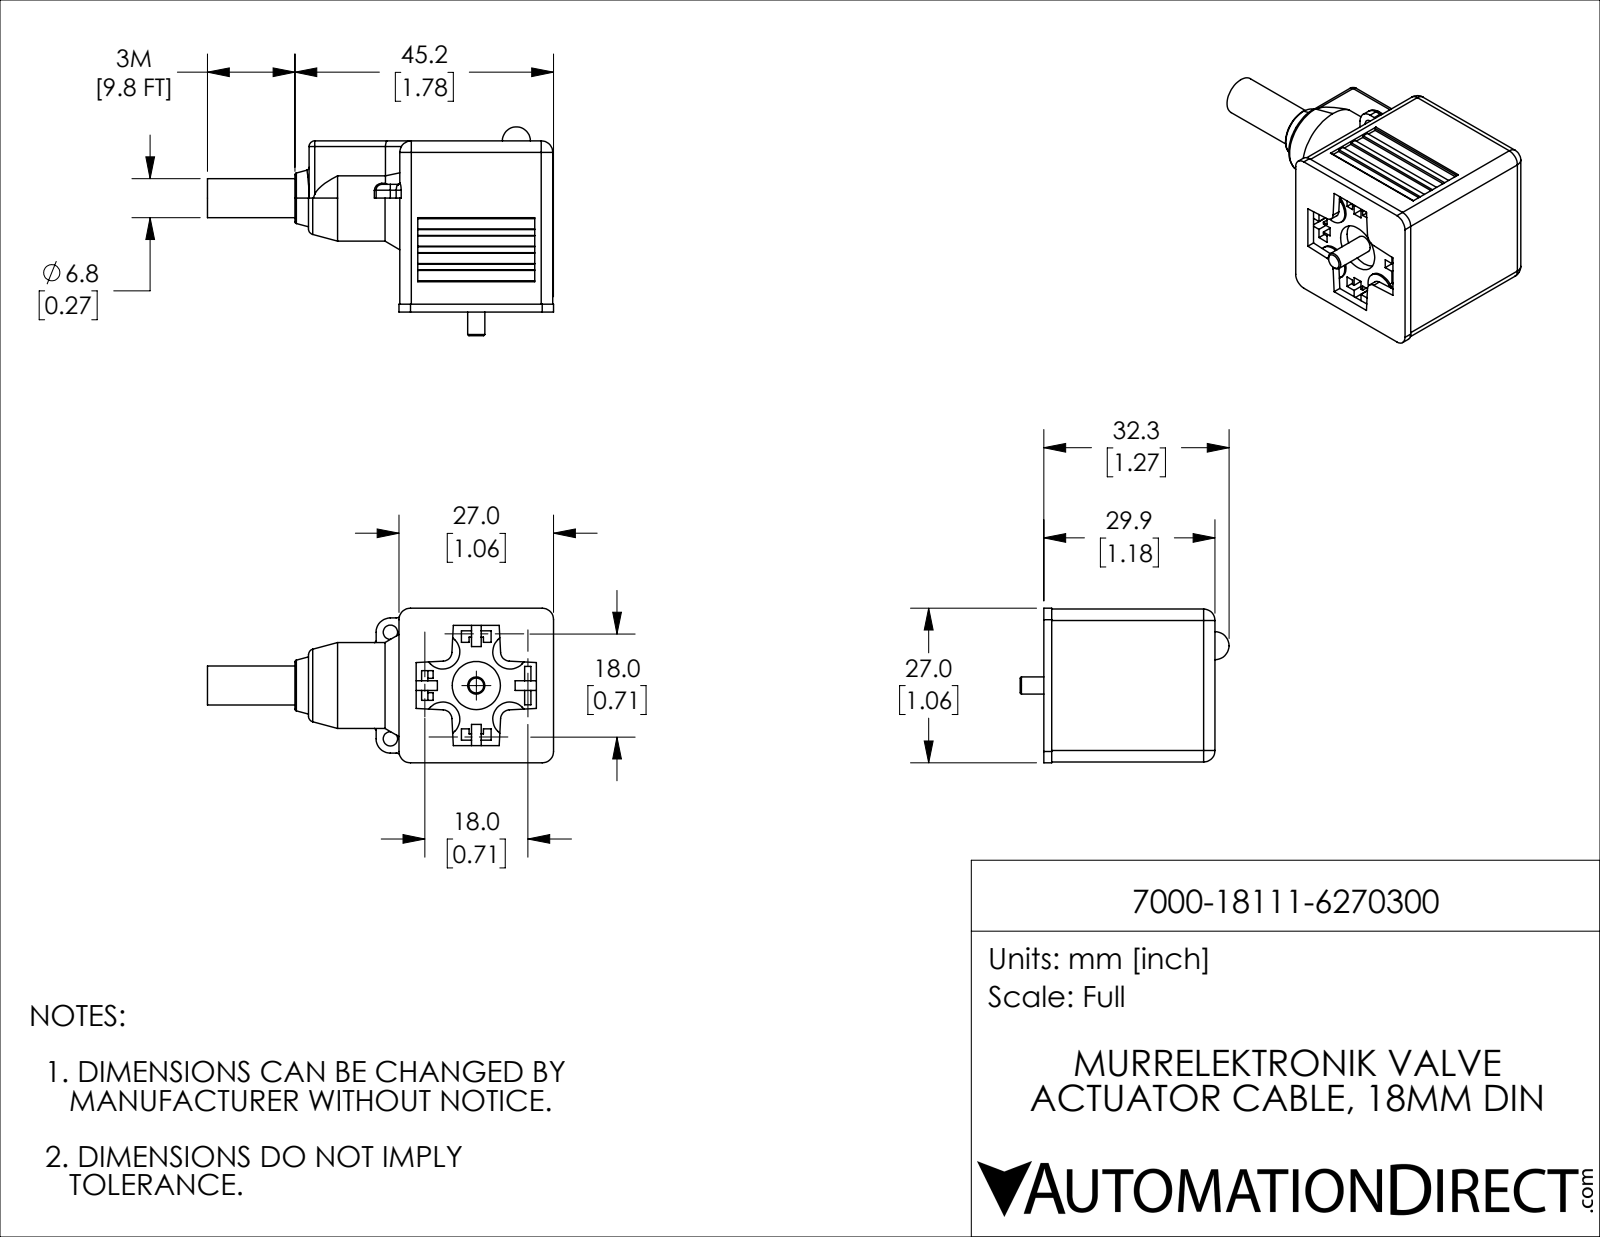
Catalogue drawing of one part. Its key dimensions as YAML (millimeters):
part_name: "7000-18111-6270300"
step_written_by: "SolidWorks 2023 (CONFIG_CONTROL_DESIGN)"
units: millimeters
bodies: {solids: 4, faces: 316, planar: 197, cylindrical: 69, other: 50}
overall_size: [60.5, 36.4, 27]
volume: 23880
surface_area: 7968
round_holes:
  - {diameter: 2.5, count: 2}
  - {diameter: 7, count: 1}
  - {diameter: 8.4, count: 1}
round_bosses_or_shafts:
  - {diameter: 6.8, count: 1}
  - {diameter: 6.5, count: 1}
  - {diameter: 3, count: 1}
partial_cylinders:
  - {radius: 2, count: 12}
  - {radius: 1, count: 10}
  - {radius: 3, count: 8}
  - {radius: 0.2, count: 4}
  - {radius: 0.7, count: 4}
  - {radius: 1.6, count: 4}
  - {radius: 0.3, count: 2}
  - {radius: 2.5, count: 2}
face_to_face_distances: [26.7, 29.9, 26.1, 12.5, 14.2, 0.6, 0.4, 1.8, 1.4, 28.5]
hole_center_spacings: [17.7, 18.6]
